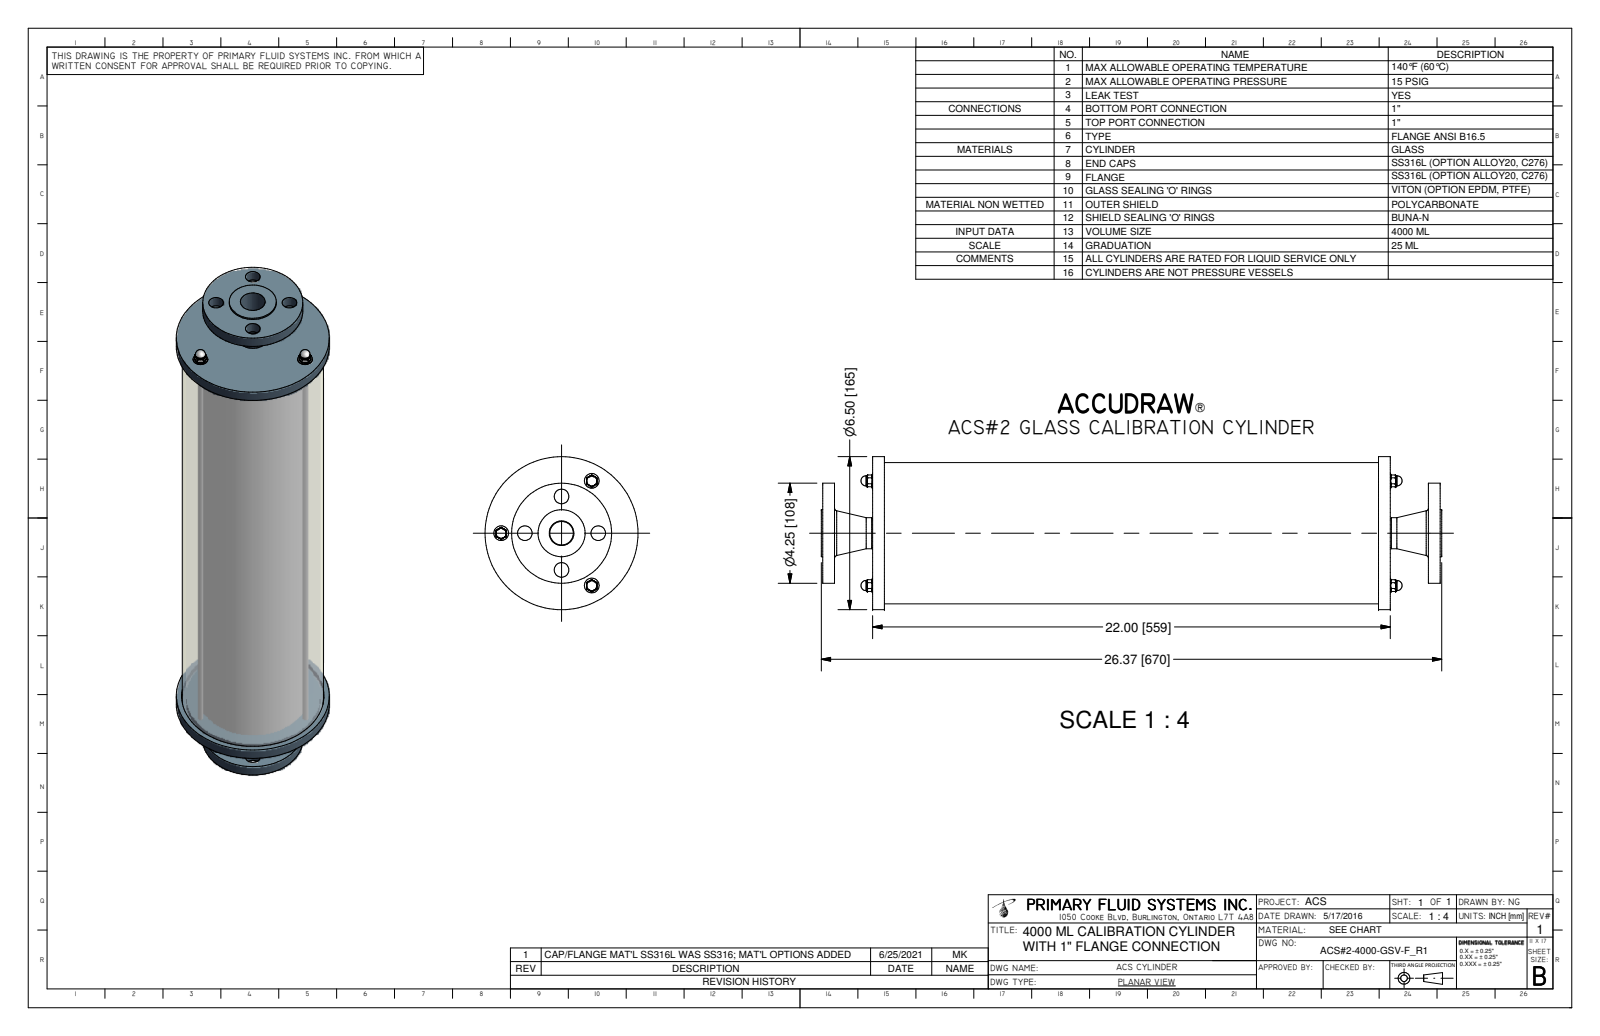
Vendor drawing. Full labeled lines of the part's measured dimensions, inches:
Part name (STEP PRODUCT): ACS#2-4000-GSV-F_R0; ACS-3-4000-METAL-S_R1; ACS-2-4000-PC_R6; ACS-1-4000-A_R0 (+4 more)
STEP written by: Autodesk Inventor 2009 (AUTOMOTIVE_DESIGN)
Units: inches
Bodies: 21 solids, 455 faces (46 planar, 57 cylindrical, 352 other)
Overall size (bounding box): 26.365 × 6.5 × 6.5
Volume: 153.6 in³ · Surface area: 1 744 in²
Round holes (diameter × count): ⌀0.62 ×4, ⌀0.18 ×3, ⌀0.266 ×3, ⌀0.281 ×3, ⌀1.049 ×1, ⌀4.134 ×1, ⌀4.625 ×1, ⌀5.75 ×1, ⌀6.05 ×1
Round bosses / shafts (diameter × count): ⌀0.625 ×3, ⌀0.25 ×3, ⌀6.5 ×1, ⌀6 ×1, ⌀5.7 ×1, ⌀4.528 ×1, ⌀4.25 ×1, ⌀4 ×1
Main face-to-face distances: 0.5, 2.12, 23.62, 22, 21.5, 2.62, 24.12, 25.741, 1.62, 23.12
Hole centre spacings: 1.56, 2.206, 2.567, 1.445, 2.24, 3.004, 3.12, 3.609
